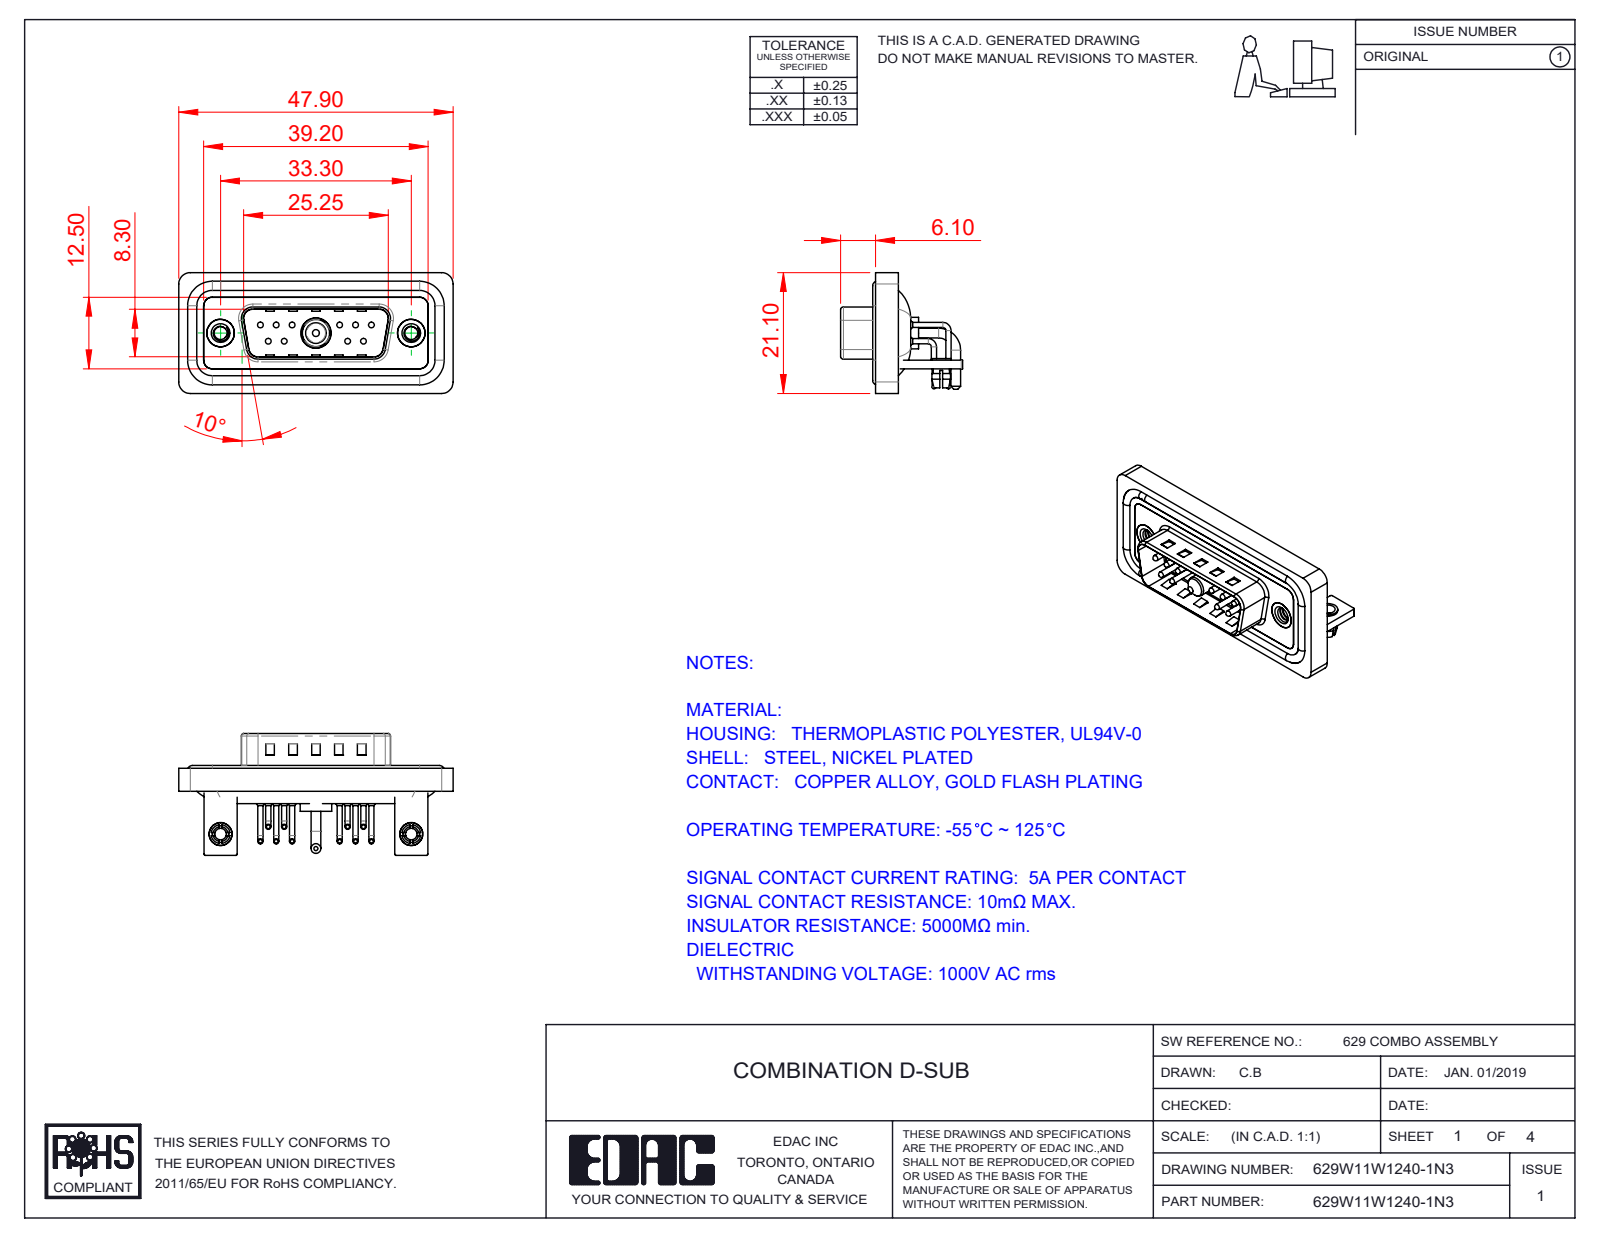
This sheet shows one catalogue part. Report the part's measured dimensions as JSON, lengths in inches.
{"part_name": "629Combo Board Lock; 629Combo Waterproof Housing_15 Contacts; 629Combo Threaded Rivet_3; 629Combo Shell Rear_15 Contacts (+7 more)", "step_written_by": "SolidWorks 2020 (CONFIG_CONTROL_DESIGN)", "units": "inches", "bodies": {"solids": 23, "faces": 1735, "planar": 904, "cylindrical": 619, "other": 212}, "overall_size": [1.886, 0.839, 0.831], "volume_in3": 0.357, "surface_area_in2": 15.54, "round_holes": [[0.079, 12], [0.03, 10], [0.063, 10], [0.089, 2], [0.098, 2], [0.126, 2], [0.157, 2], [0.189, 2], [0.197, 2], [0.191, 1], [0.209, 1]], "round_bosses_or_shafts": [[0.035, 20], [0.059, 10], [0.039, 10], [0.026, 10], [0.063, 4], [0.193, 2], [0.157, 2], [0.134, 2]], "partial_cylinders_radius": [[0.079, 21], [0.059, 18], [0.01, 16], [0.04, 10], [0.02, 9], [0.063, 8], [0.039, 7], [0.024, 4]], "face_to_face_distances": [0.016, 0.031, 0.059, 0.114, 0.083, 0.043, 0.063, 0.047, 0.146, 0.161], "hole_center_spacings": [0.124, 0.109, 0.545, 0.436, 0.654, 0.198, 0.198, 0.218]}
